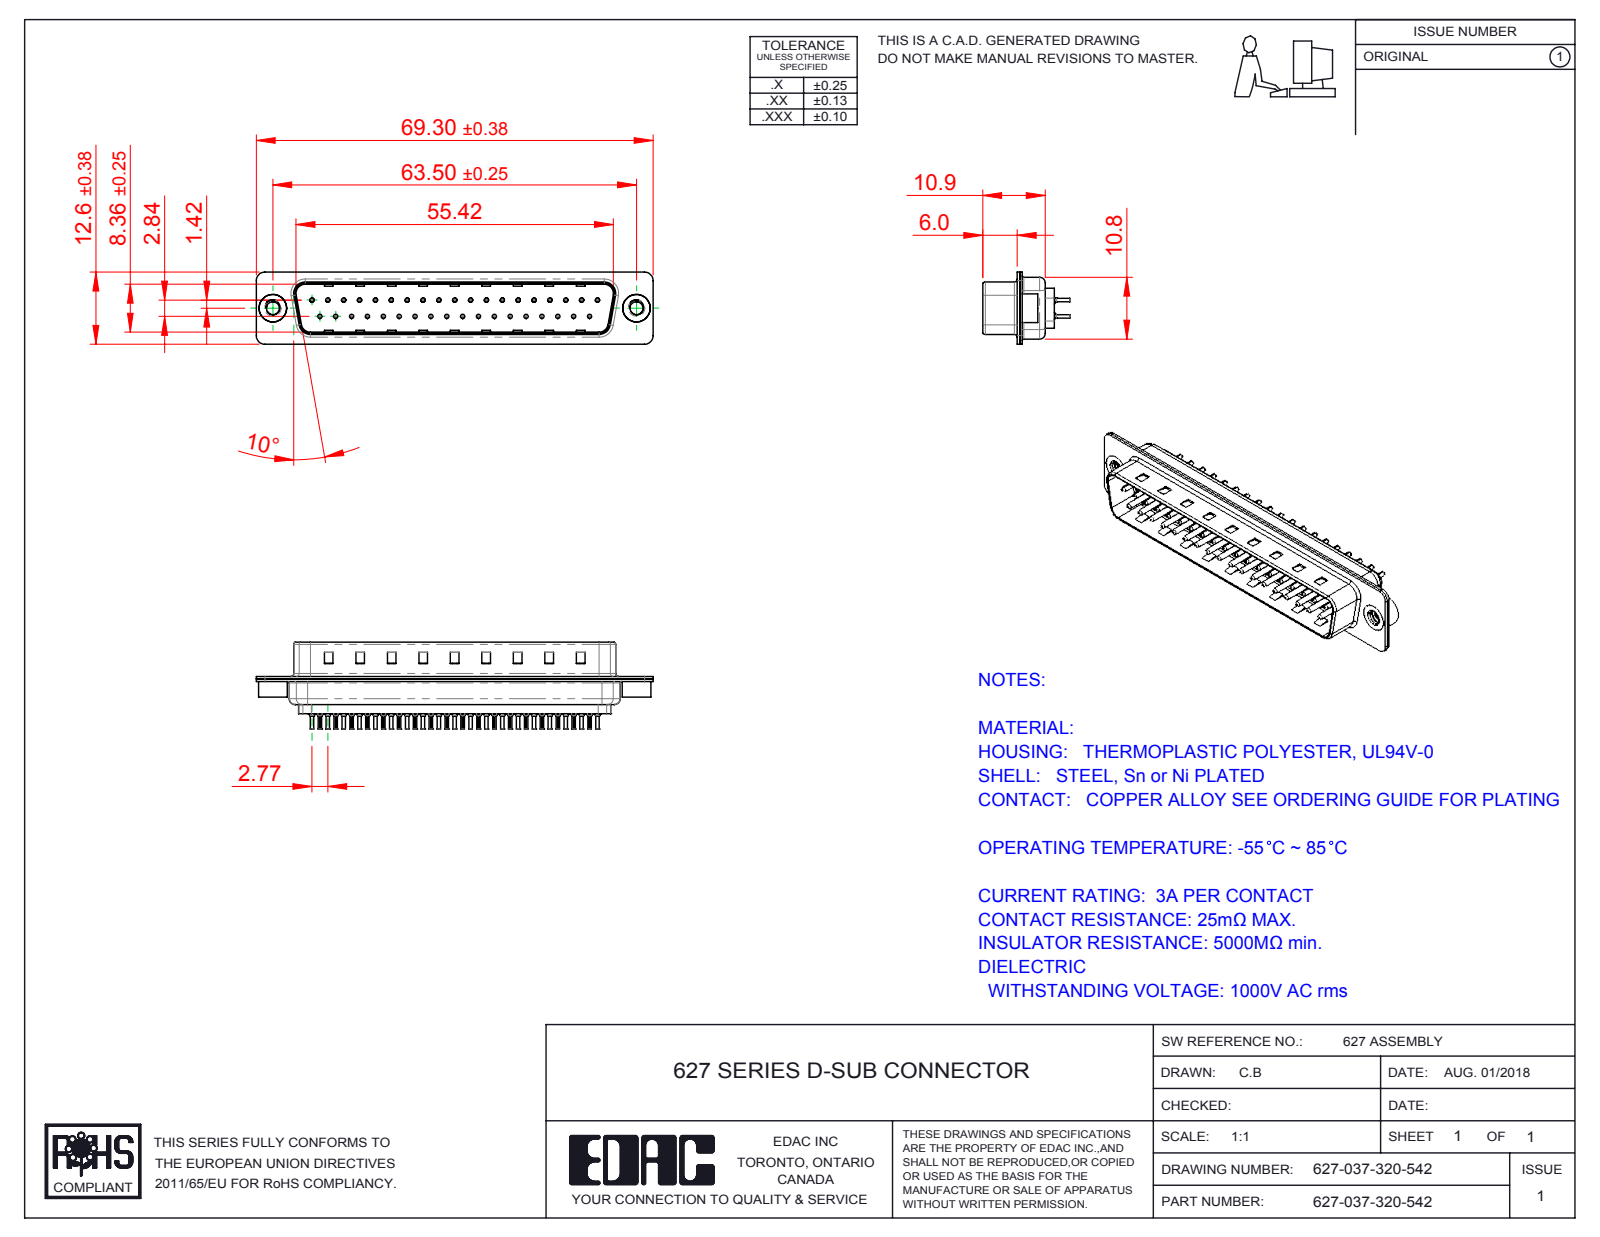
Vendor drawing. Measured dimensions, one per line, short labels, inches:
name: 627 4-40 Threaded Rivet; 627-037-320-542; 627 Contact Row 1_20L; 627 Shell Front_37 Contacts (+3 more)
written by: SolidWorks 2016 (CONFIG_CONTROL_DESIGN)
unit: in
bodies: 42 solids, 4038 faces (1091 planar, 1510 cylindrical, 1437 other)
size: 2.728 × 0.598 × 0.496
volume: 0.225 in³; area: 16.22 in²
holes: 37× ⌀0.008, 37× ⌀0.014, 37× ⌀0.043, 37× ⌀0.063, 2× ⌀0.089, 2× ⌀0.157, 2× ⌀0.189
bosses: 37× ⌀0.079, 37× ⌀0.059, 37× ⌀0.03, 37× ⌀0.024, 2× ⌀0.197, 2× ⌀0.193
rounds: 74× R0.004, 16× R0.059, 12× R0.079, 8× R0.02, 8× R0.063, 4× R0.01, 4× R0.024, 4× R0.026
face distances: 0.016, 0.032, 0.377, 0.018, 0.345, 0.059, 0.035, 0.055, 0.238, 0.017
hole spacings: 0.124, 0.109, 0.218, 0.327, 0.198, 0.398, 0.436, 0.503
